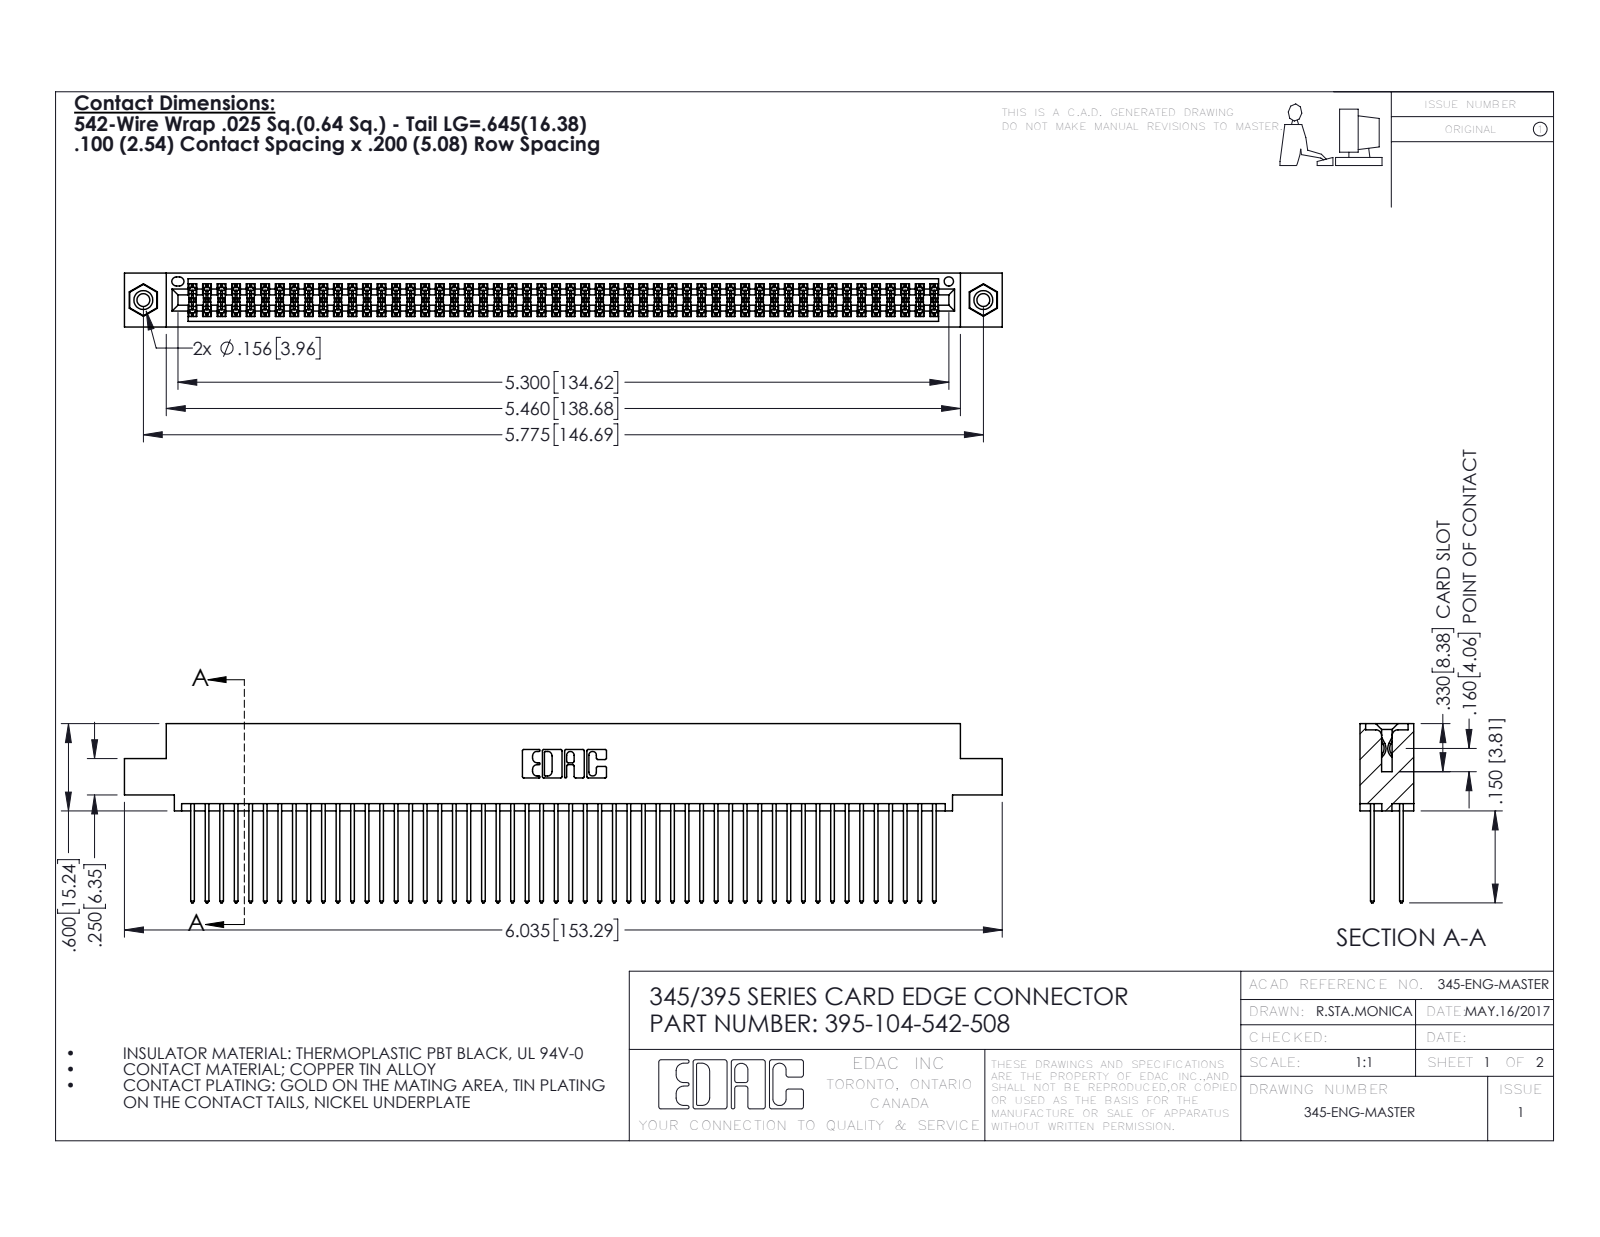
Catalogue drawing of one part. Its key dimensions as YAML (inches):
part_name: "345-292-001_345-293-142; 345-250-001_345-250-003-102; 345 Part_0.110 Offset - 0.156 Dia-TI; 395-104-542-508"
step_written_by: "SolidWorks 2016 (CONFIG_CONTROL_DESIGN)"
units: inches
bodies: {solids: 107, faces: 5390, planar: 3548, cylindrical: 1826, other: 16}
overall_size: [6.035, 1.232, 0.37]
volume: 0.939
surface_area: 39.23
round_holes:
  - {diameter: 0.089, count: 2}
  - {diameter: 0.125, count: 2}
  - {diameter: 0.156, count: 2}
  - {diameter: 0.064, count: 1}
round_bosses_or_shafts:
  - {diameter: 0.155, count: 2}
partial_cylinders:
  - {radius: 0.006, count: 156}
  - {radius: 0.01, count: 104}
  - {radius: 0.01, count: 22}
  - {radius: 0.007, count: 6}
  - {radius: 0.031, count: 6}
  - {radius: 0.026, count: 3}
  - {radius: 0.014, count: 2}
  - {radius: 0.019, count: 2}
face_to_face_distances: [0.072, 0.298, 0.2, 0.098, 0.272, 0.025, 0.225, 0.37, 0.175, 0.149]
hole_center_spacings: [0.27, 5.539, 5.775]
